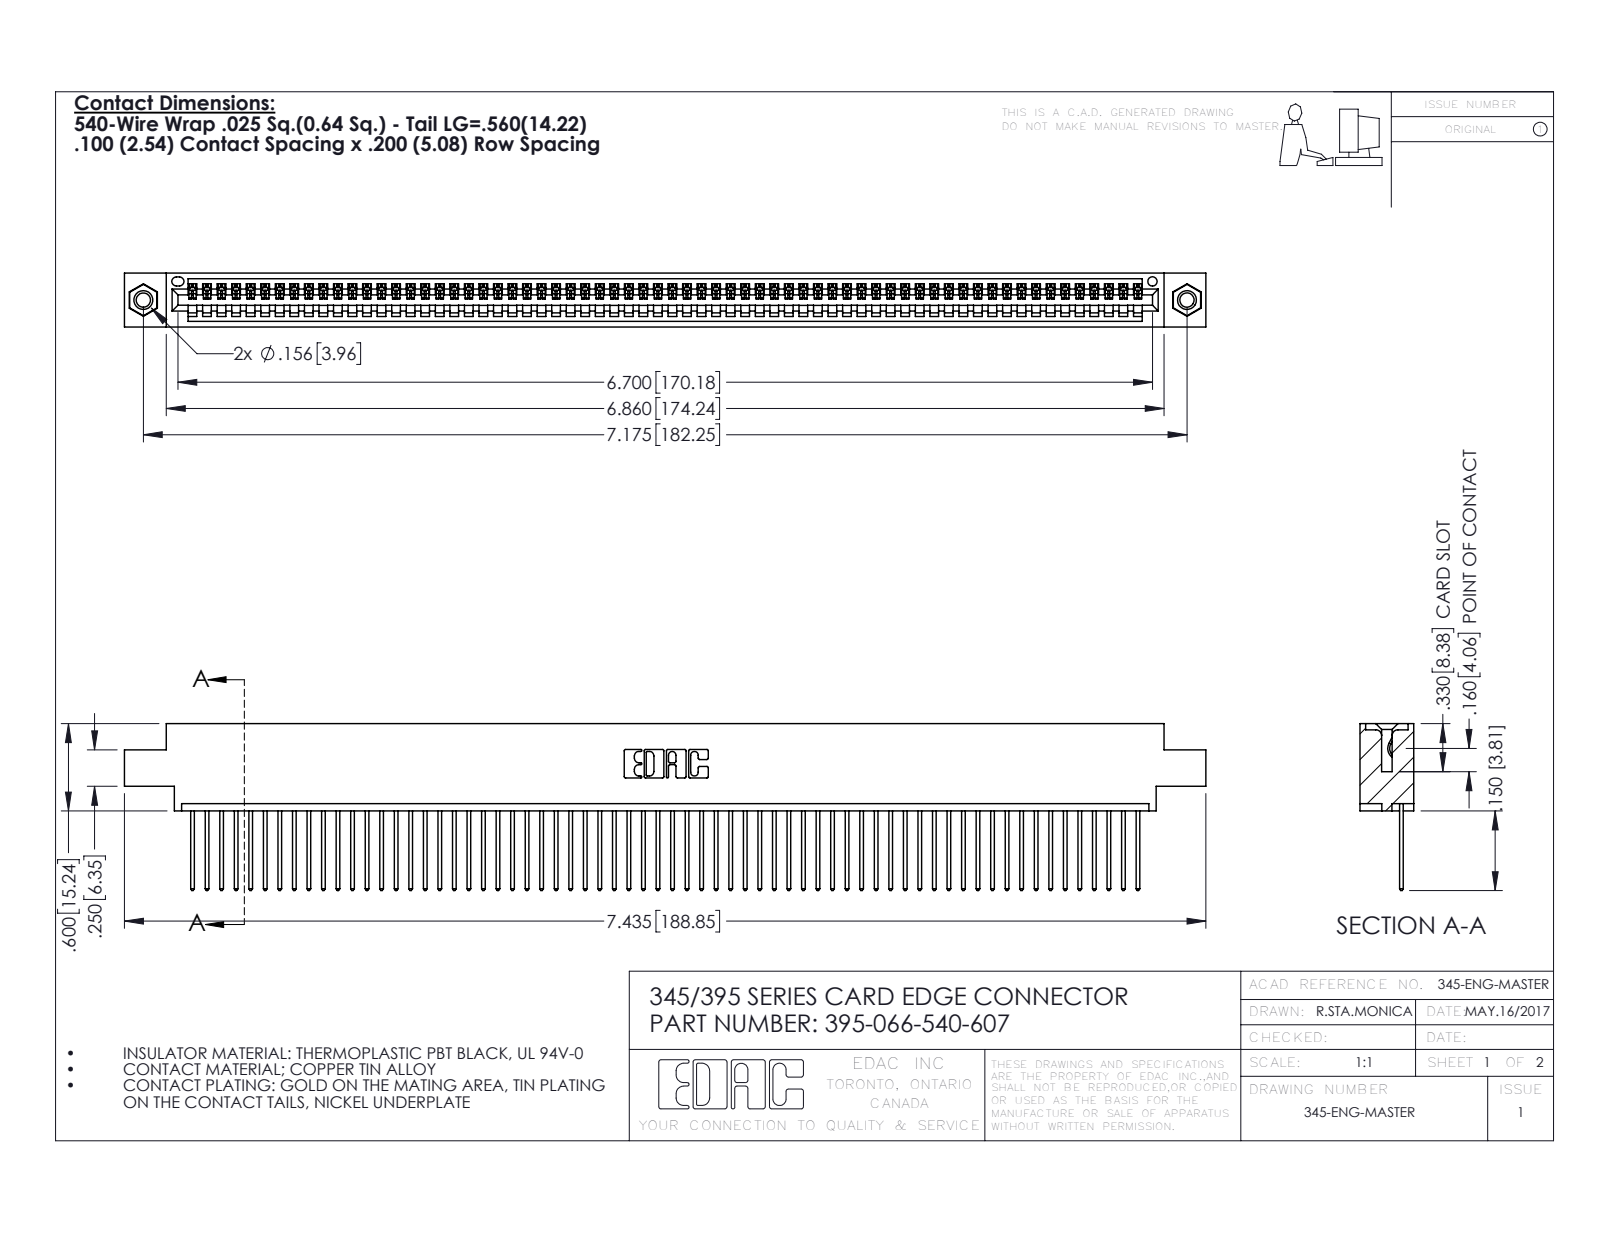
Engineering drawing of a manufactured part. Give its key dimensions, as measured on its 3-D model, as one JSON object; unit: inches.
{"part_name": "395-066-540-607; 345-292-001_345-293-140; 345 Part_0.170 Offset - 0.156 Dia-TI; 345-250-001_345-250-005-103", "step_written_by": "SolidWorks 2016 (CONFIG_CONTROL_DESIGN)", "units": "inches", "bodies": {"solids": 69, "faces": 4018, "planar": 2756, "cylindrical": 1246, "other": 16}, "overall_size": [7.435, 1.147, 0.37], "volume_in3": 1.104, "surface_area_in2": 39.02, "round_holes": [[0.098, 2], [0.125, 2], [0.156, 2], [0.064, 1]], "round_bosses_or_shafts": [[0.155, 2]], "partial_cylinders_radius": [[0.006, 132], [0.01, 132], [0.01, 22], [0.007, 6], [0.031, 6], [0.026, 3], [0.031, 2], [0.04, 2]], "face_to_face_distances": [0.072, 0.298, 0.37, 0.098, 0.272, 0.025, 0.2, 0.225, 0.175, 0.149], "hole_center_spacings": [0.27, 6.939, 7.175]}
